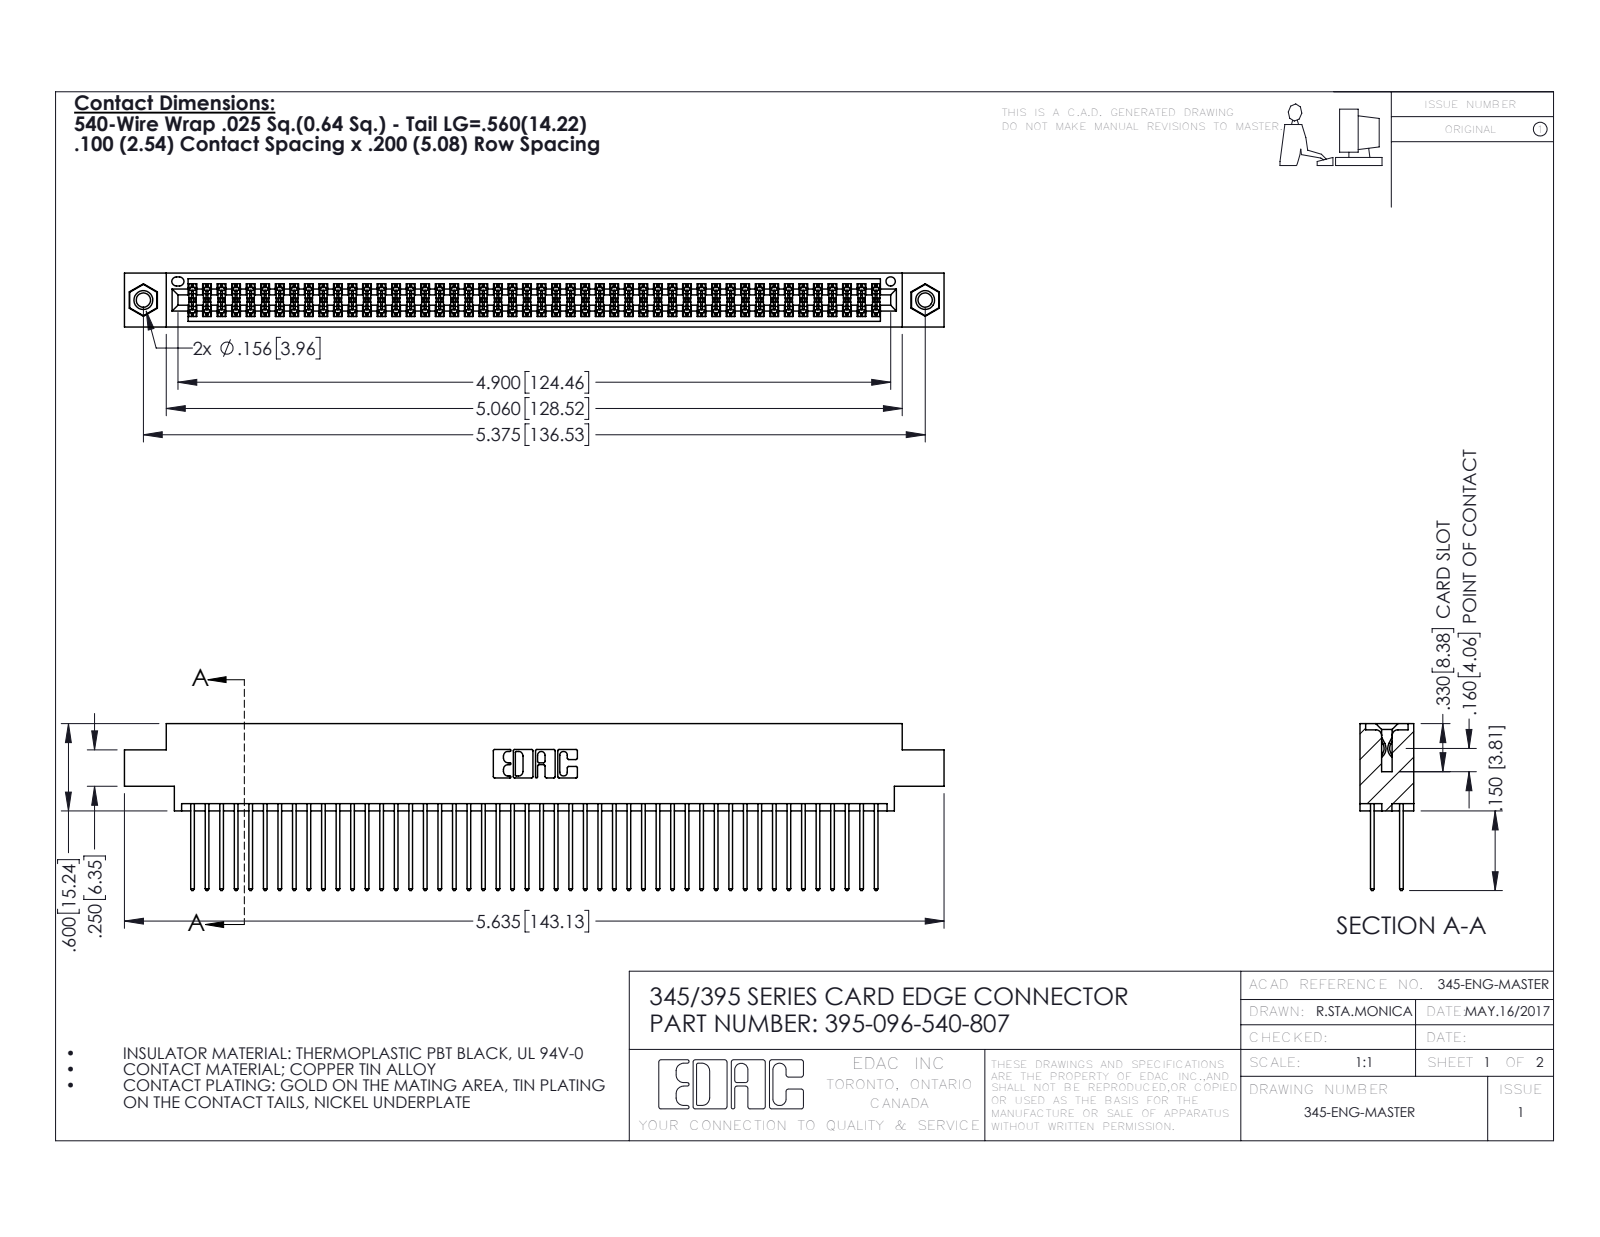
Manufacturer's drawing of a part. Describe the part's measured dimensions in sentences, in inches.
The part is named "395-096-540-807; 345 Part_0.170 Offset - 0.156 Dia-TI; 345-292-001_345-293-140; 345-250-001_345-250-005-103". Its 3-D file was written by "SolidWorks 2016 (CONFIG_CONTROL_DESIGN)". It is 99 solids with 4990 faces: 3284 planar, 1690 cylindrical and 16 other. Overall it measures 5.635 by 1.147 by 0.37 inches. Its volume is 0.866 cubic inches and its surface area 35.59 square inches. Round holes: 2 of diameter 0.098, 2 of diameter 0.125, 2 of diameter 0.156, 1 of diameter 0.064. Round bosses or shafts: 2 of diameter 0.155. Partial cylindrical surfaces (rounded edges, fillets, slot ends): 144 of radius 0.006, 96 of radius 0.01, 22 of radius 0.01, 6 of radius 0.007, 6 of radius 0.031, 3 of radius 0.026, 2 of radius 0.014, 2 of radius 0.019. The main face-to-face distances are 0.072, 0.298, 0.2, 0.098, 0.272, 0.025, 0.37, 0.225, 0.175, 0.149. The hole center spacings are 0.27, 5.139, 5.375.
